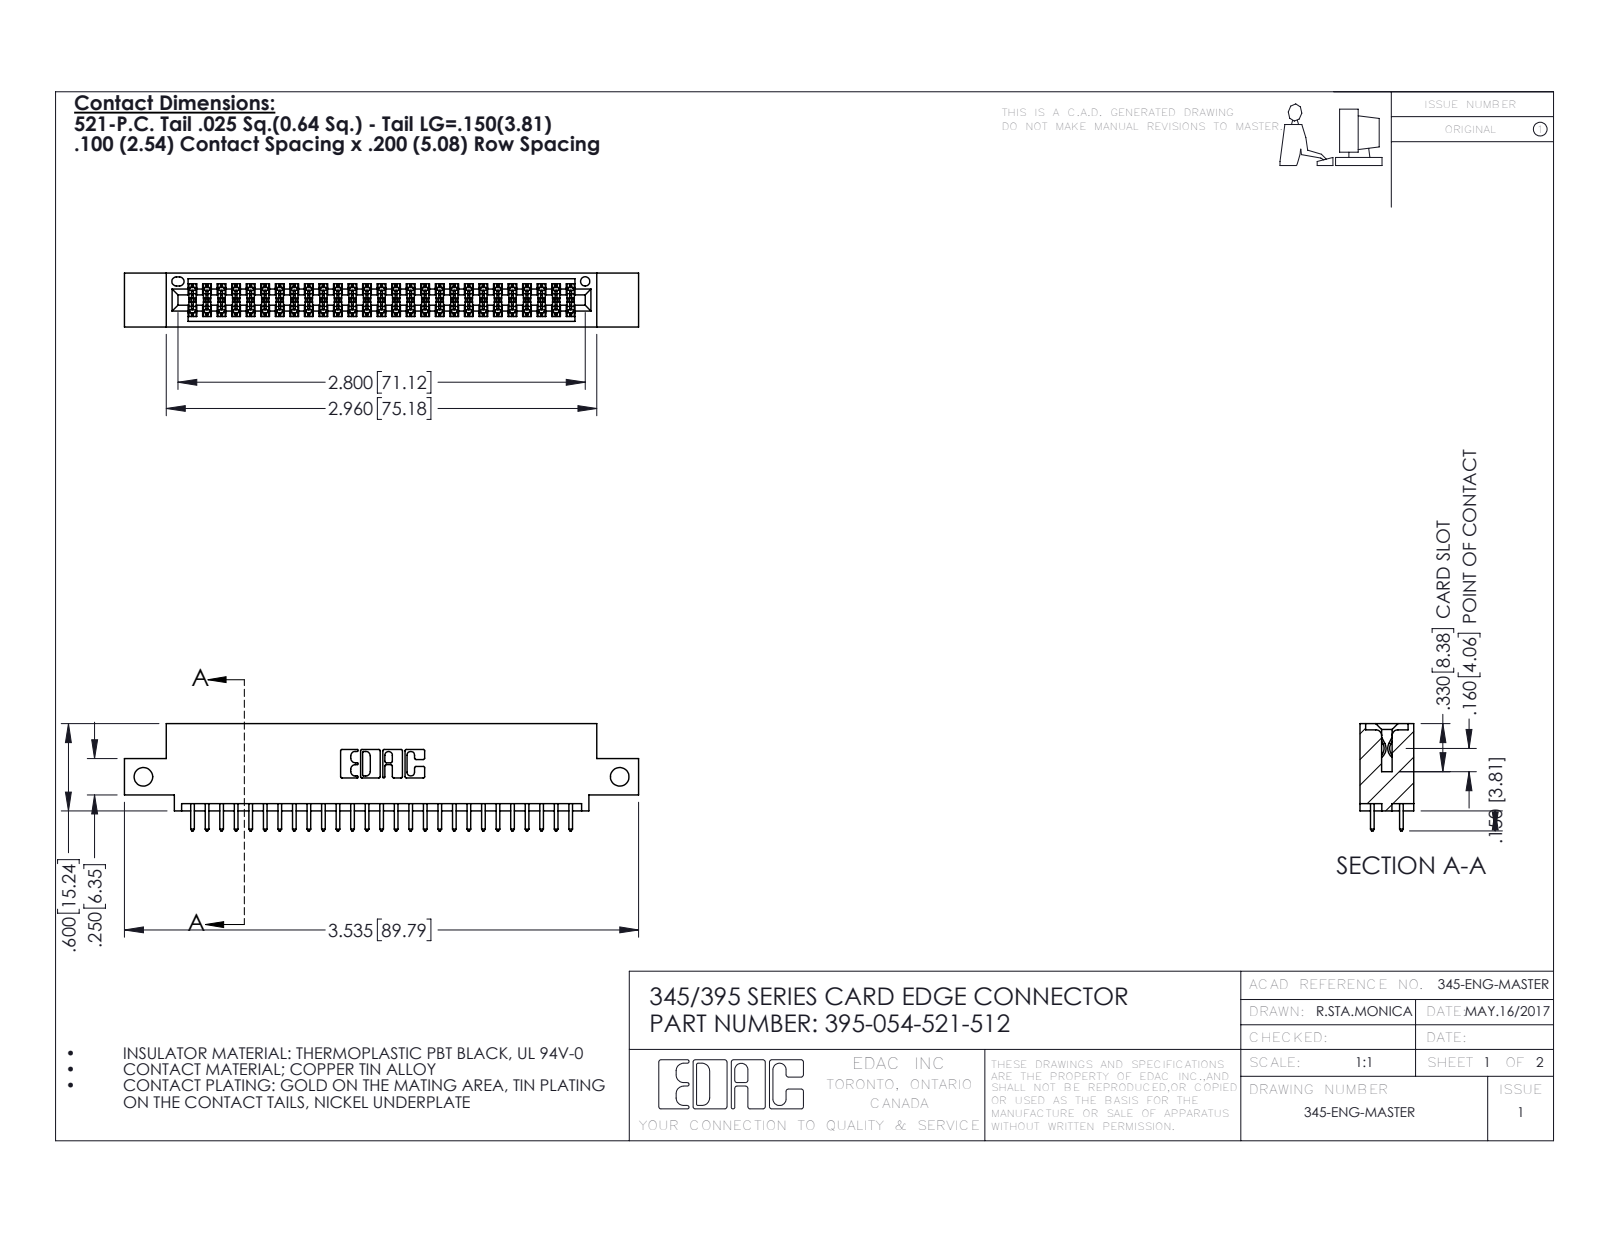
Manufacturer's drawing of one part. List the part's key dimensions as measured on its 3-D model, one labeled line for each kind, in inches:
Part name (STEP PRODUCT): 345-292-001_345-293-121; 395-054-521-512; 345 Part_0.110 Offset - Side Mount
STEP written by: SolidWorks 2016 (CONFIG_CONTROL_DESIGN)
Units: inches
Bodies: 55 solids, 2830 faces (1866 planar, 964 cylindrical, 0 other)
Overall size (bounding box): 3.535 × 0.737 × 0.37
Volume: 0.513 in³ · Surface area: 18.51 in²
Round holes (diameter × count): ⌀0.128 ×2, ⌀0.064 ×1
Partial cylindrical surfaces — rounded edges, fillets, slot ends (radius × count): R0.006 ×81, R0.01 ×54, R0.01 ×22, R0.007 ×6, R0.031 ×6, R0.026 ×3, R0.014 ×2, R0.019 ×2
Main face-to-face distances: 0.298, 0.072, 0.2, 0.37, 0.098, 0.272, 0.025, 0.225, 0.175, 0.149
Hole centre spacings: 3.275
